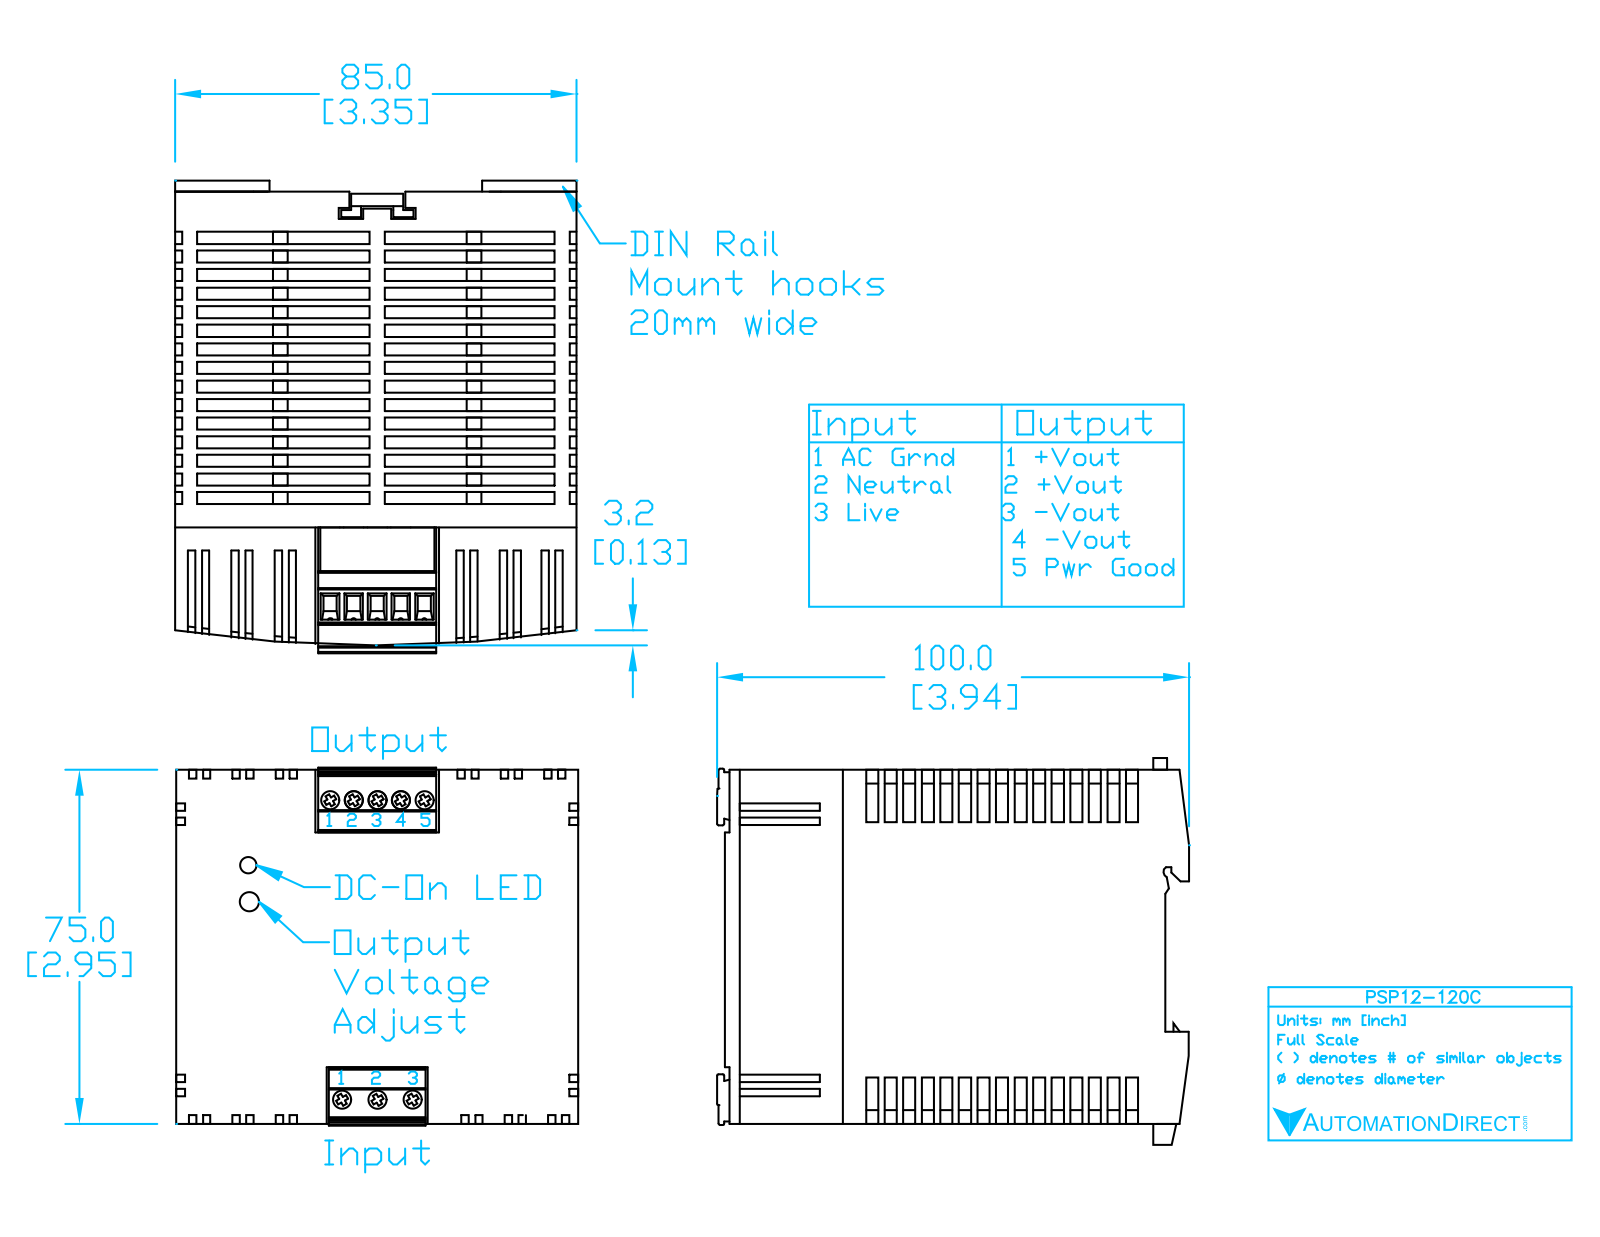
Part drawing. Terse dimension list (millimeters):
name: PSP12-120C
written by: SolidWorks 2011 (CONFIG_CONTROL_DESIGN)
unit: mm
bodies: 4 solids, 488 faces (417 planar, 0 cylindrical, 71 other)
size: 100.5 × 85 × 80
volume: 701 409 mm³; area: 71 783 mm²
face distances: 75, 85, 68.85, 68.95, 14.16, 60.84, 59.67, 45.51, 15.33, 2.48
